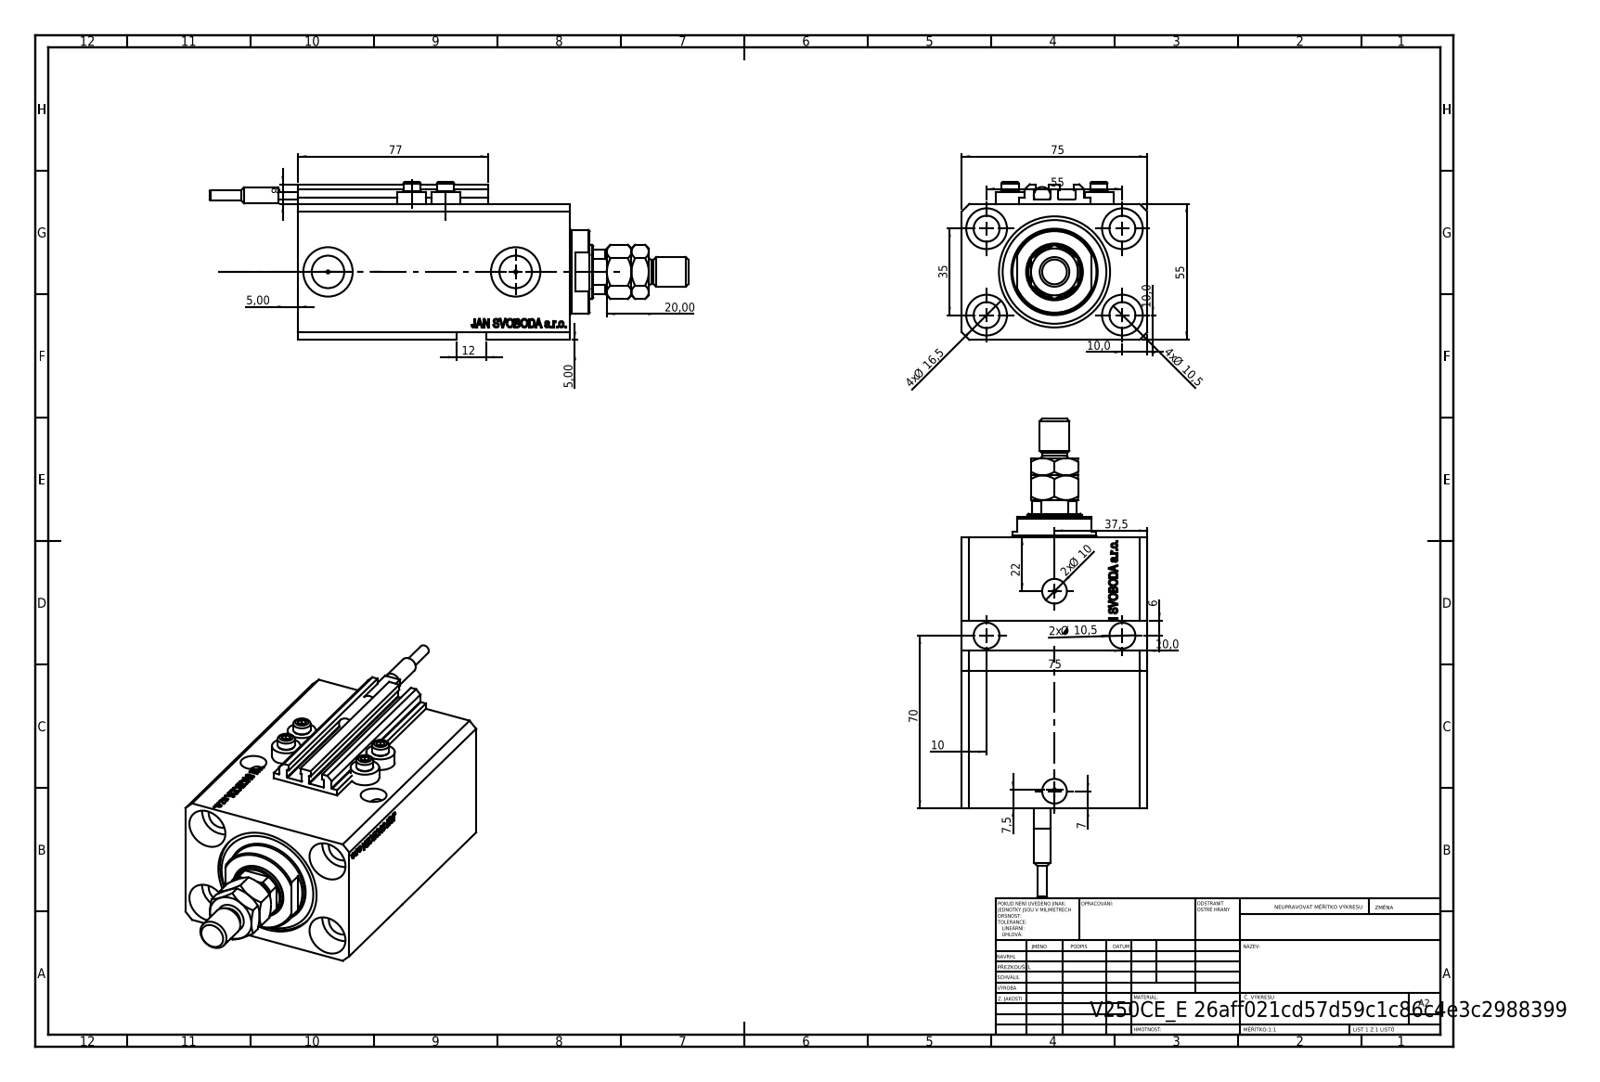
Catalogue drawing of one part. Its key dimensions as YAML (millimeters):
part_name: "ALLEN BOLT V250CE; SWITCH_V250CE; V250CE_VC_E; V250CE_E (+2 more)"
step_written_by: "SolidWorks 2019 (CONFIG_CONTROL_DESIGN)"
units: millimeters
bodies: {solids: 10, faces: 1139, planar: 545, cylindrical: 136, other: 458}
overall_size: [193.9, 75, 64]
volume: 396515
surface_area: 100420
round_holes:
  - {diameter: 10.5, count: 7}
  - {diameter: 1.25, count: 4}
  - {diameter: 4, count: 4}
  - {diameter: 16.5, count: 4}
  - {diameter: 10, count: 2}
  - {diameter: 13.16, count: 2}
  - {diameter: 20, count: 2}
  - {diameter: 22, count: 1}
  - {diameter: 32, count: 1}
  - {diameter: 45, count: 1}
round_bosses_or_shafts:
  - {diameter: 11.6, count: 4}
  - {diameter: 7, count: 4}
  - {diameter: 34, count: 1}
  - {diameter: 12, count: 1}
  - {diameter: 10, count: 1}
  - {diameter: 6.8, count: 1}
  - {diameter: 6.5, count: 1}
  - {diameter: 4, count: 1}
partial_cylinders:
  - {radius: 0.2, count: 10}
  - {radius: 10.5, count: 1}
face_to_face_distances: [55, 75, 3, 110, 82.9, 27.1, 9.9, 57, 73, 100.1]
hole_center_spacings: [32.6, 55, 13.6, 14.09, 25.81, 32.87, 33.62, 35]
